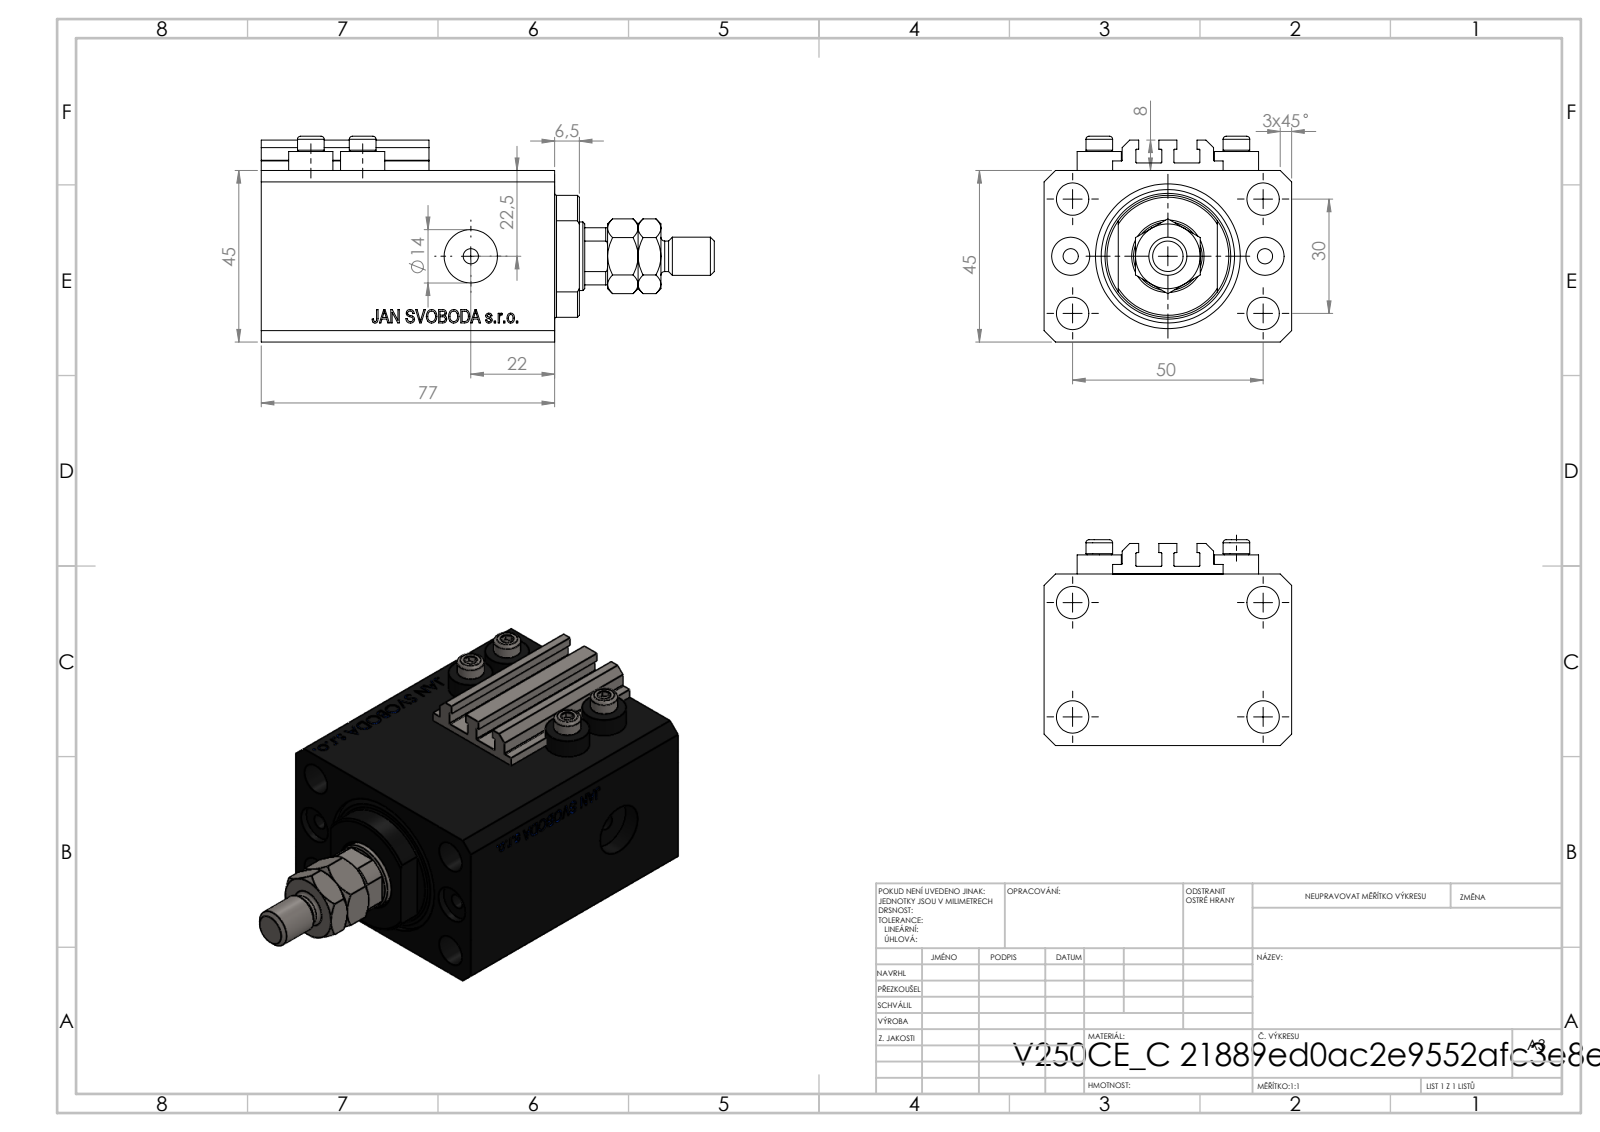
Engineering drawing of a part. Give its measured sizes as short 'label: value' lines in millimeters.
name: V250CE_VC_C; ALLEN BOLT V250CE; V250CE_C_VCP; V250CE_C_Body (+1 more)
written by: SolidWorks 2019 (CONFIG_CONTROL_DESIGN)
unit: mm
bodies: 9 solids, 1082 faces (518 planar, 90 cylindrical, 474 other)
size: 118.9 × 65 × 54
volume: 216 375 mm³; area: 61 162 mm²
holes: 8× ⌀4, 5× ⌀8.5, 2× ⌀10, 2× ⌀14, 1× ⌀18, 1× ⌀25, 1× ⌀38
bosses: 4× ⌀11.6, 4× ⌀7, 1× ⌀10, 1× ⌀8
rounds: 10× R0.2, 1× R8.5, 1× R16
face distances: 45, 65, 51.9, 77, 25.1, 6.9, 70.1, 3, 47, 6
hole spacings: 15.01, 29.15, 52.68, 13.6, 25.5, 30, 36, 38.48
